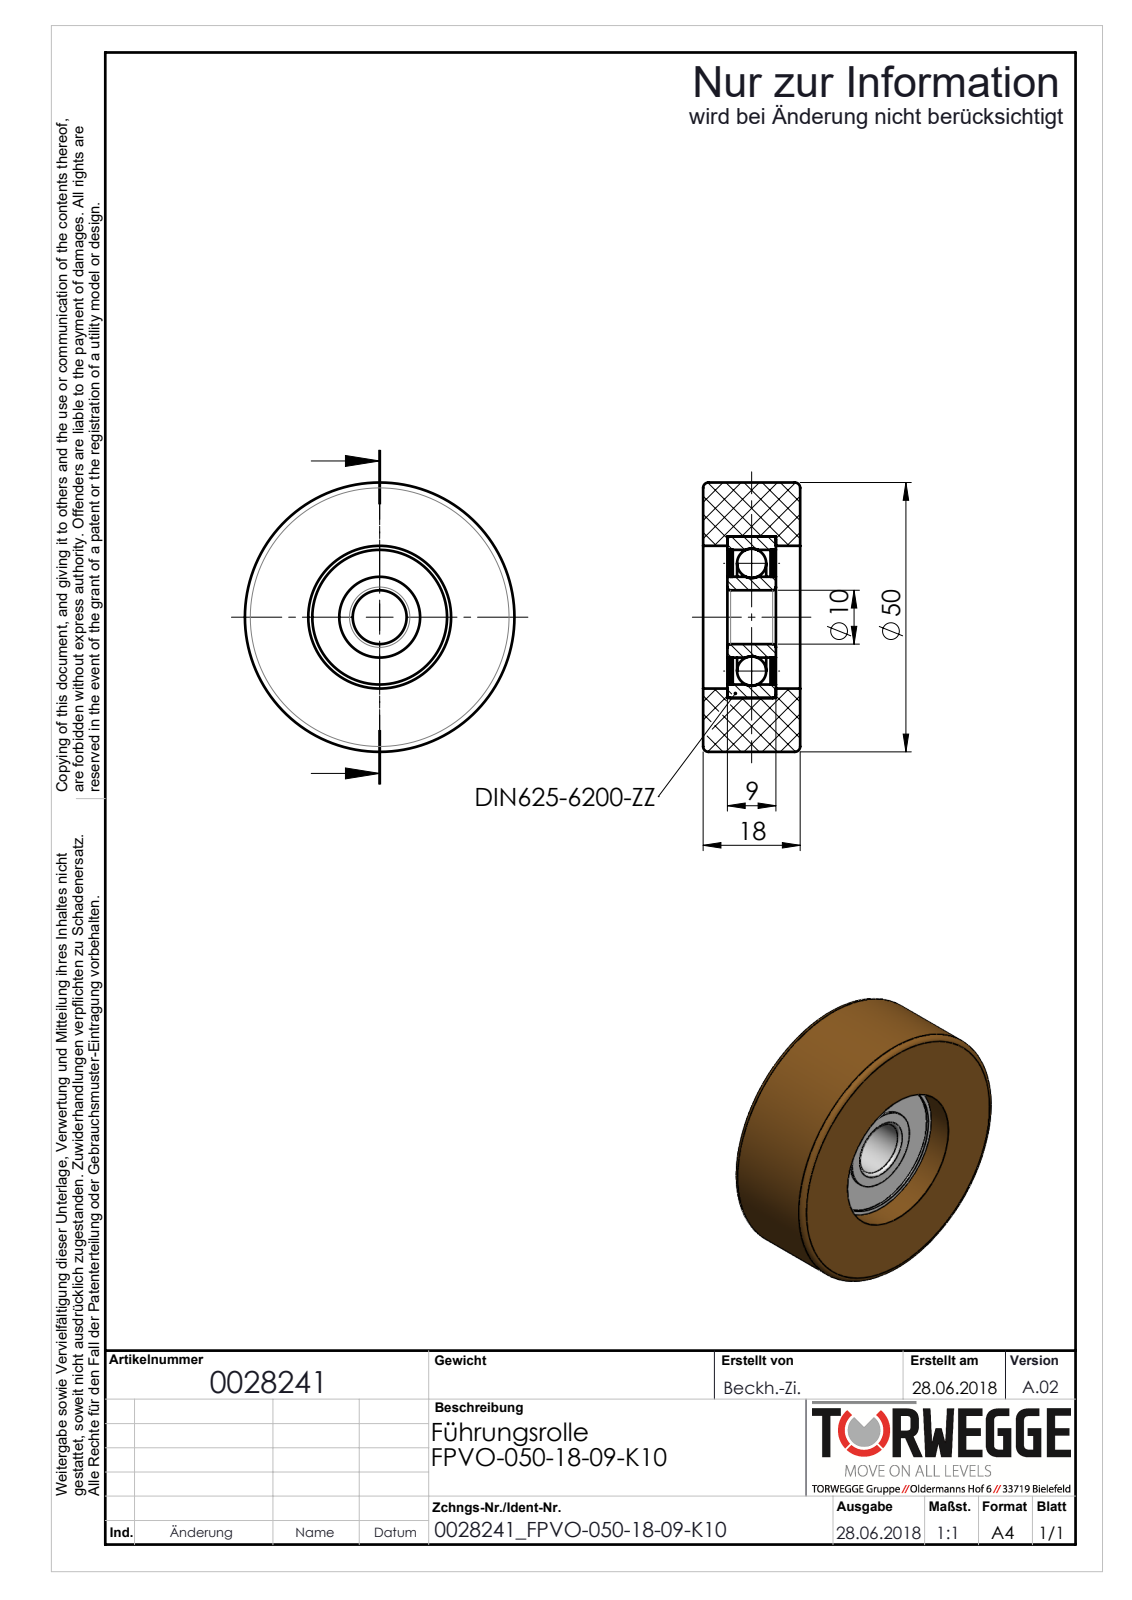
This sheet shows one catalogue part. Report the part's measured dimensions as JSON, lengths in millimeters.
{"part_name": "0028241_FPVO-050-18-09-K10", "step_written_by": "SolidWorks 2018 (AUTOMOTIVE_DESIGN)", "units": "millimeters", "bodies": {"solids": 0, "faces": 32, "planar": 8, "cylindrical": 16, "other": 8}, "overall_size": [50, 50, 18], "round_holes": [[10, 1], [25, 1], [26.5, 1]], "round_bosses_or_shafts": [[50, 1], [15, 1]], "face_to_face_distances": [18, 5, 13, 4.5, 13.5, 0.5, 8.5, 8, 9]}
